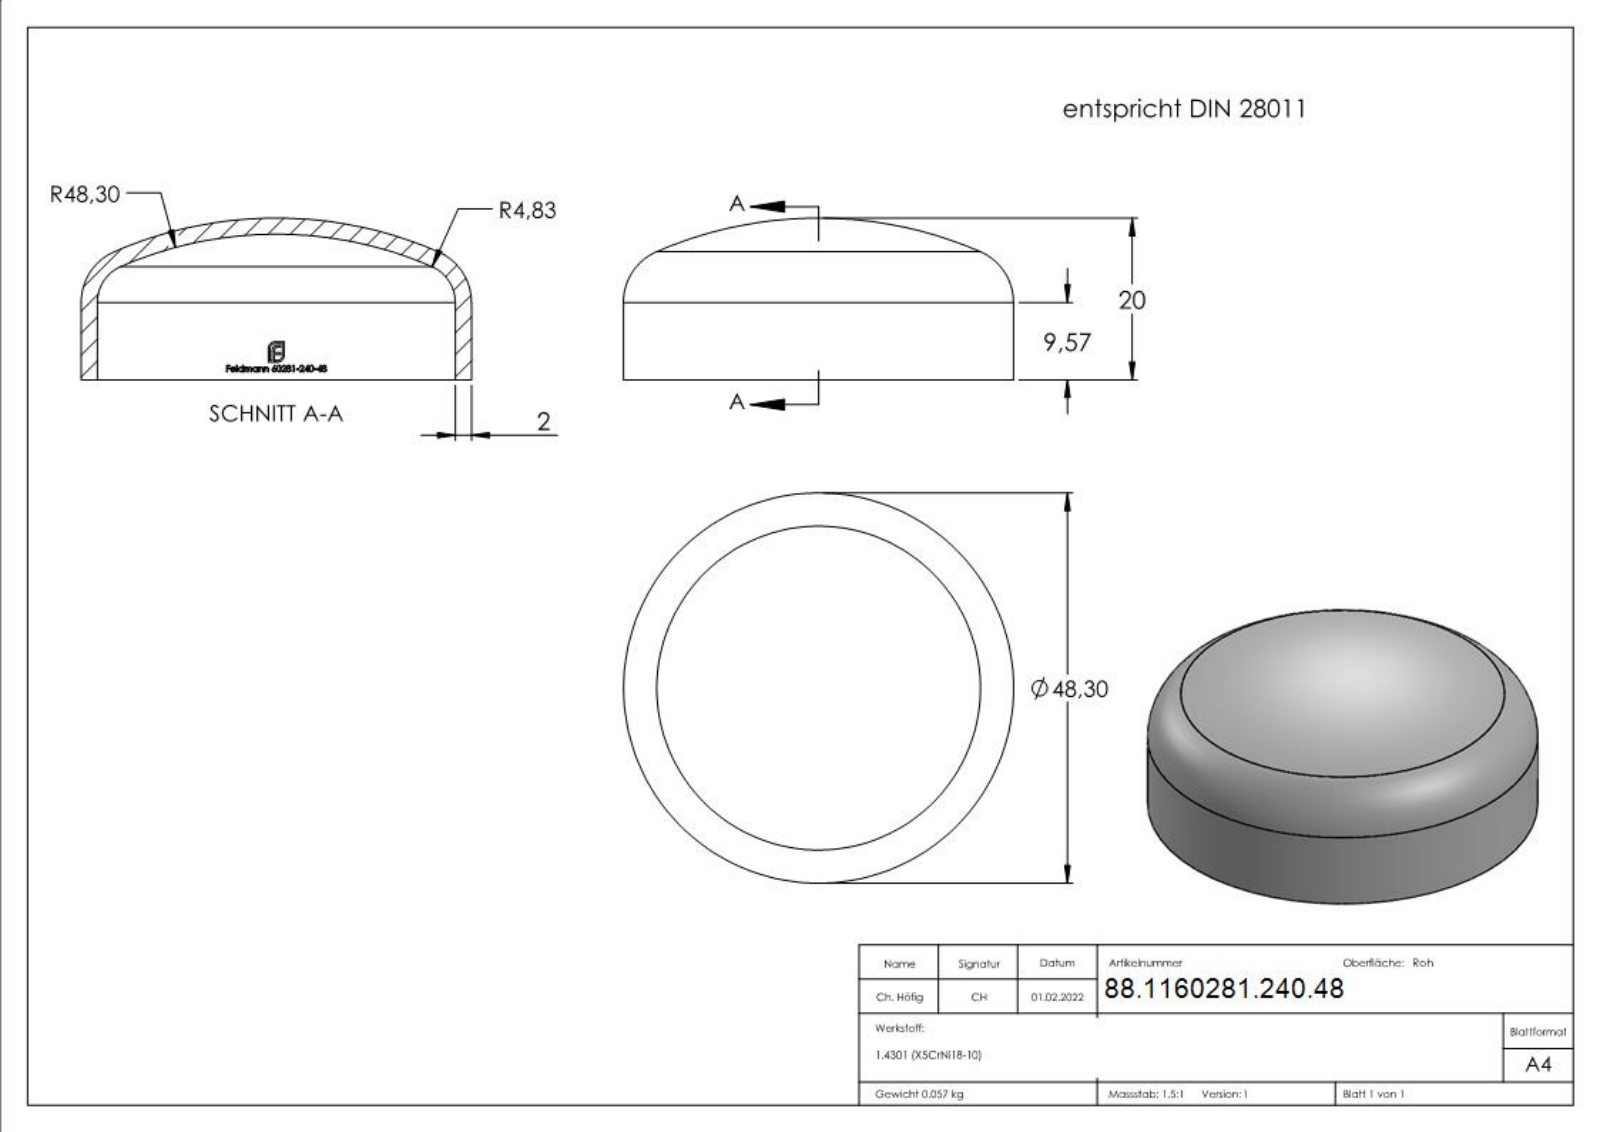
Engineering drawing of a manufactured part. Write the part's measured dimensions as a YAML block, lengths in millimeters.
part_name: "60281-240-48"
step_written_by: "SolidWorks 2018 (CONFIG_CONTROL_DESIGN)"
units: millimeters
bodies: {solids: 1, faces: 325, planar: 132, cylindrical: 44, other: 149}
overall_size: [48.3, 48.3, 20]
volume: 7182
surface_area: 7490
round_holes:
  - {diameter: 44.3, count: 1}
round_bosses_or_shafts:
  - {diameter: 48.3, count: 1}
partial_cylinders:
  - {radius: 22.25, count: 1}
face_to_face_distances: [1.76, 3.37, 1.96, 2.45, 3.31, 1, 1.02, 3.12, 1.35, 2.32]
